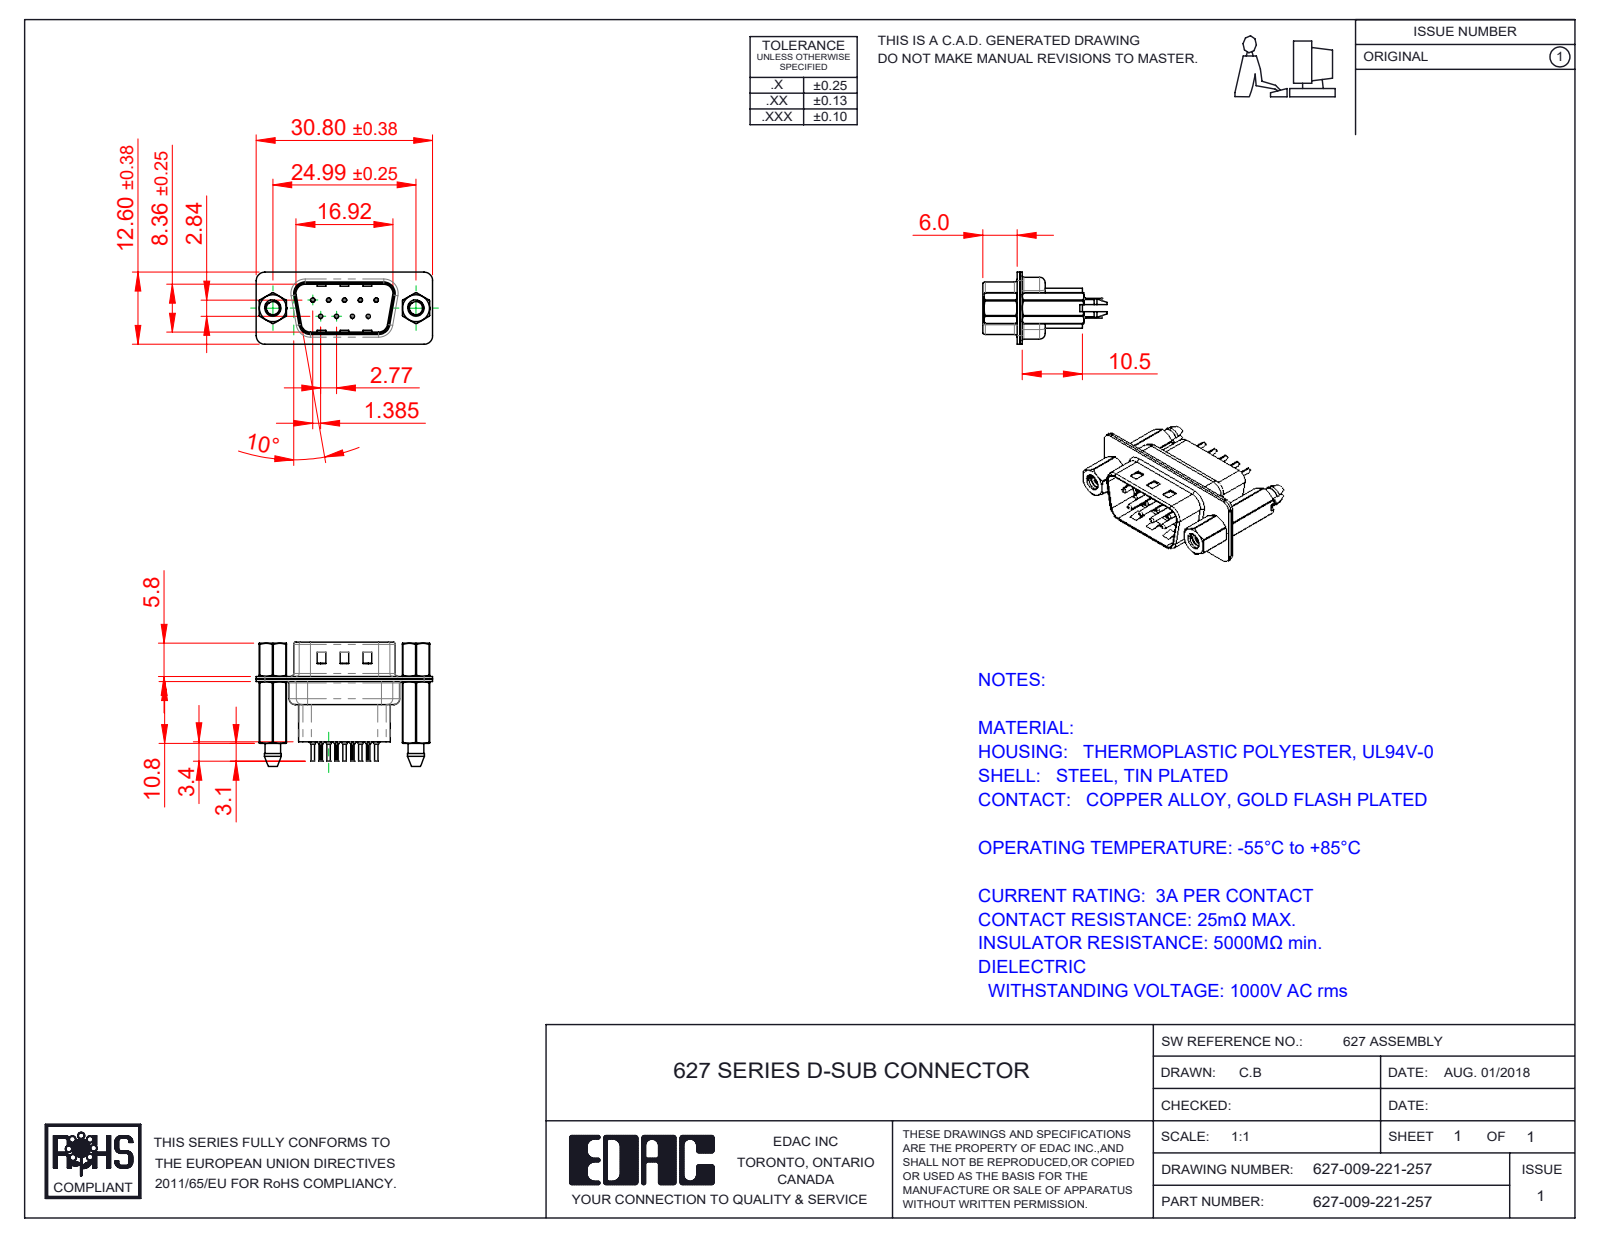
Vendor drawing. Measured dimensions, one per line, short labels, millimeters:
name: 627 4-40 Hex Standoff; 627 Housing_09 HP; 627 Contact Row 1_21H; 627 4-40 Threaded Boardlock_HP (+4 more)
written by: SolidWorks 2020 (CONFIG_CONTROL_DESIGN)
unit: mm
bodies: 16 solids, 1426 faces (377 planar, 602 cylindrical, 447 other)
size: 30.8 × 21.7 × 12.6
volume: 2 235 mm³; area: 5 764 mm²
holes: 9× ⌀0.2, 9× ⌀0.35, 9× ⌀1.1, 9× ⌀1.6, 2× ⌀2.26, 2× ⌀2.29, 2× ⌀4, 2× ⌀4.8
bosses: 9× ⌀2, 9× ⌀1.5, 9× ⌀0.75, 9× ⌀0.6, 2× ⌀4.9, 2× ⌀2.79
rounds: 20× R1.5, 18× R0.1, 12× R2, 10× R1.6, 8× R0.5, 4× R0.25, 4× R0.6, 4× R0.65
face distances: 0.45, 0.4, 0.9, 4.76, 0.82, 9.58, 1.4, 1.5, 0.68, 7.68
hole spacings: 3.16, 2.77, 5.54, 5.03, 5.04, 8.31, 7.48, 7.49
